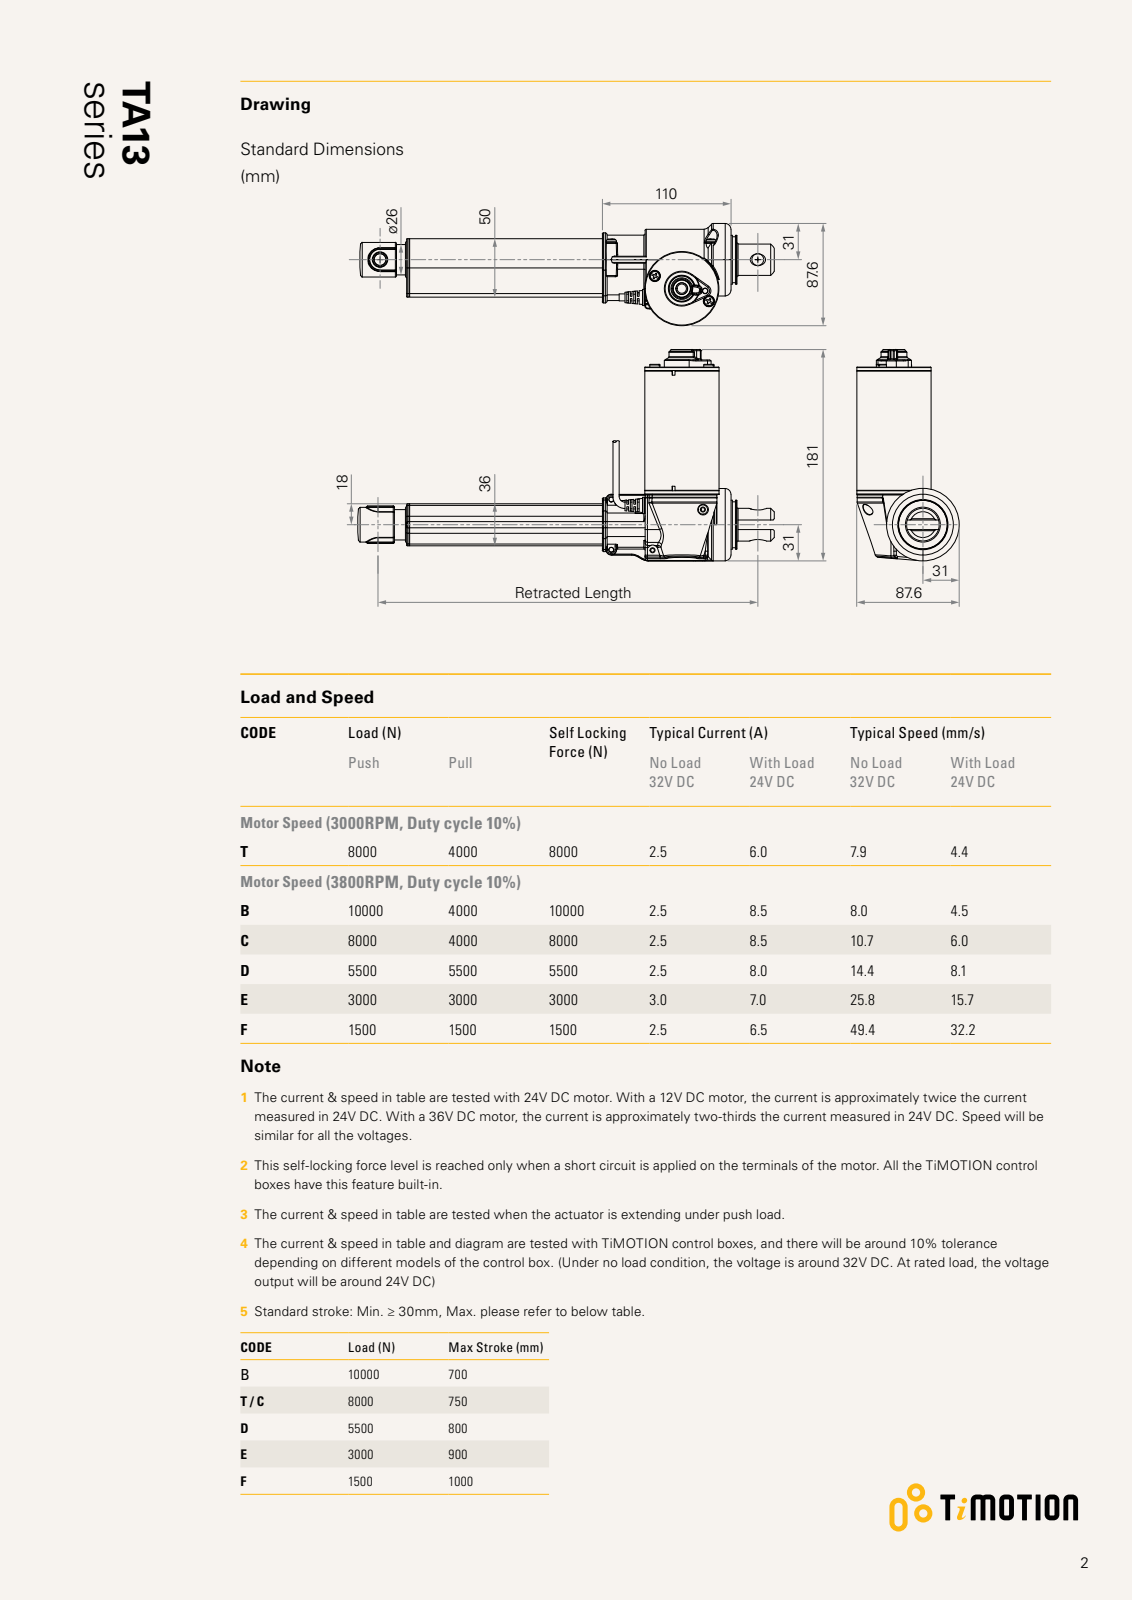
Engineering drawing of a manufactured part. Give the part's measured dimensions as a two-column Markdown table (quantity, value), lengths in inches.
| quantity | value |
| --- | --- |
| part name | 3D_TA13-745 |
| STEP written by | SolidWorks 2010 (CONFIG_CONTROL_DESIGN) |
| units | inches |
| bodies | 2 solids, 296 faces (83 planar, 95 cylindrical, 118 other) |
| overall size | 30.315 × 6.457 × 3.465 |
| volume | 83.85 in³ |
| surface area | 225.3 in² |
| round holes (diameter × count) | 0.323 × 1, 0.402 × 1 |
| round bosses / shafts (diameter × count) | 2.52 × 1, 2.441 × 1, 2.047 × 1, 1.65 × 1, 1.547 × 1, 1.102 × 1, 1.024 × 1 |
| partial cylindrical surfaces (radius × count) | 0.02 × 20, 0.039 × 12, 0.059 × 3, 0.197 × 2, 0.315 × 2, 0.394 × 2, 0.079 × 1, 0.224 × 1 |
| main face-to-face distances | 0.118, 1.142, 0.323, 5.122, 4.799, 4.331, 3.189, 0.197, 4.528, 3.386 |
| hole center spacings | 29.331 |
